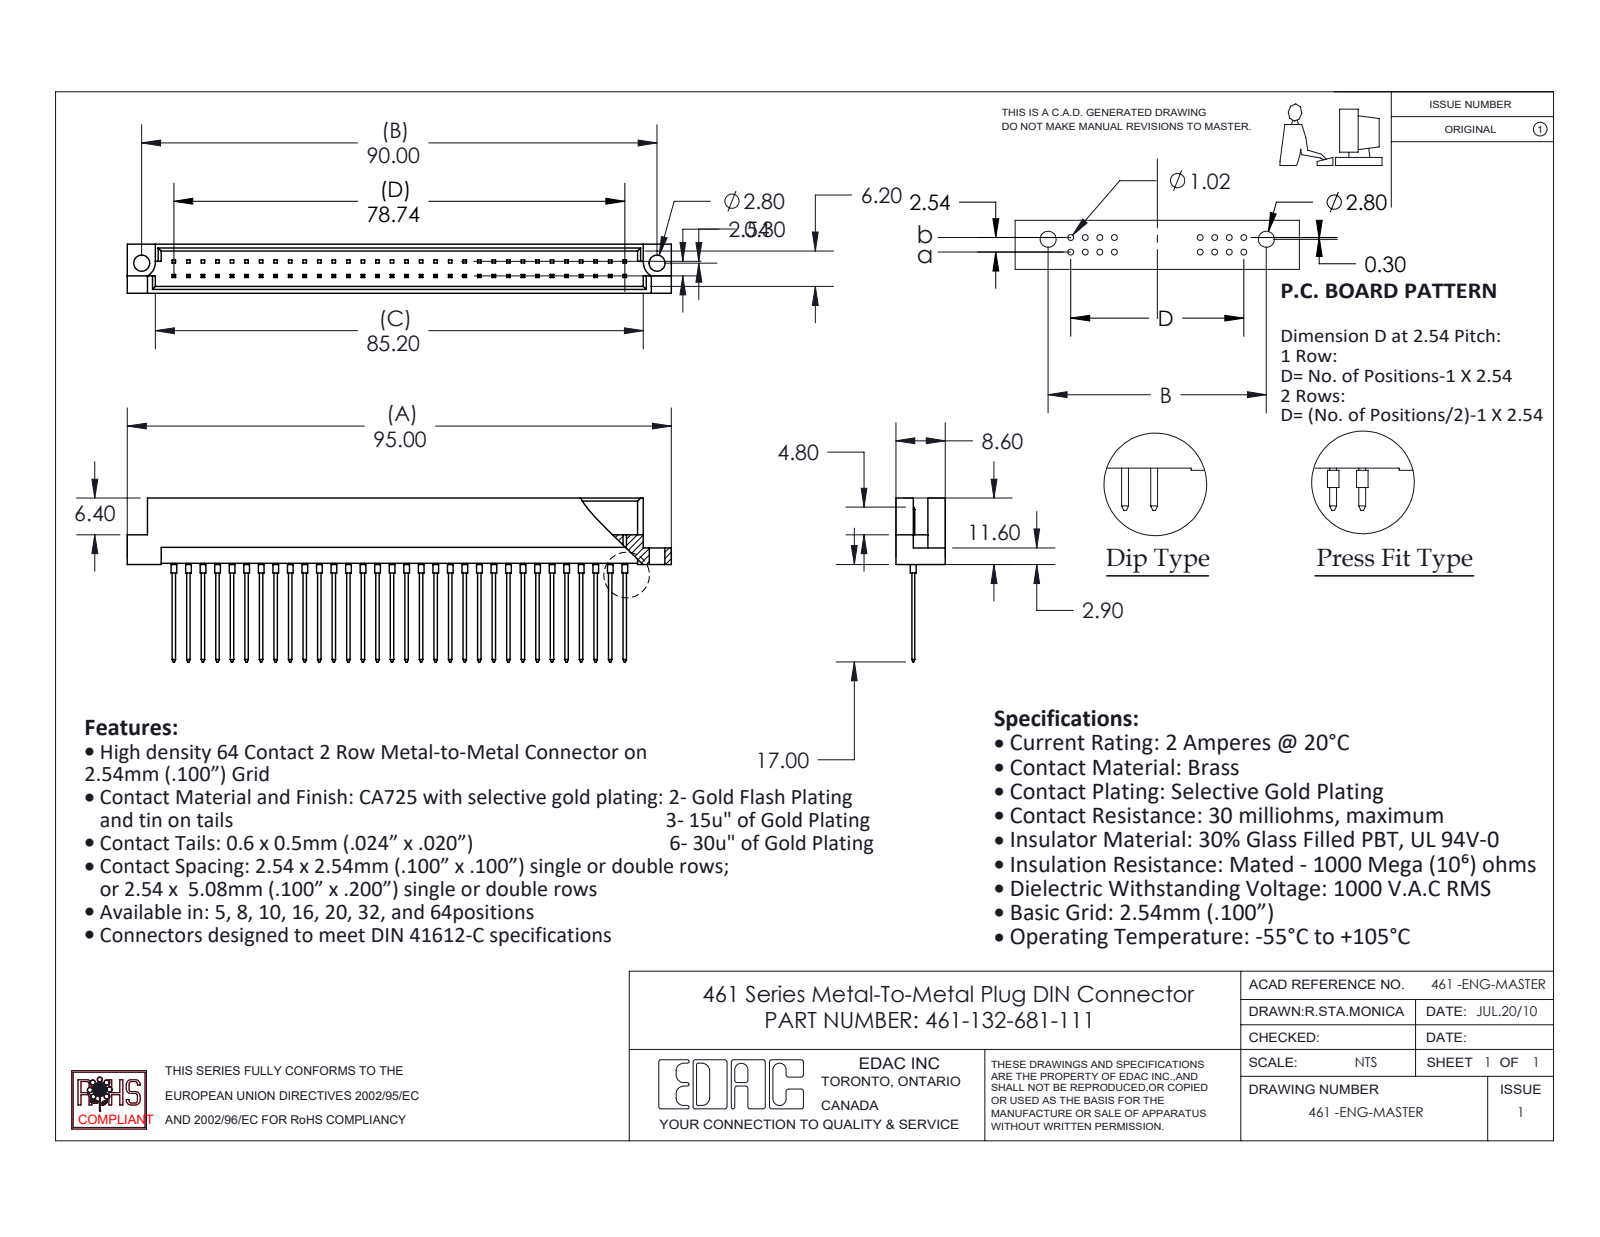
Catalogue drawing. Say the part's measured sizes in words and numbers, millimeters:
The part is named "461-290_81; 461-132-681-111; 461 Part_64". Its 3-D file was written by "SolidWorks 2020 (CONFIG_CONTROL_DESIGN)". It is 33 solids with 1009 faces: 938 planar, 71 cylindrical and 0 other. Overall it measures 95 by 28.6 by 8.6 millimeters. Its volume is 4 936 cubic millimeters and its surface area 7 636 square millimeters. Round holes: 2 of diameter 2.8. Round bosses or shafts: 32 of diameter 1. Partial cylindrical surfaces (rounded edges, fillets, slot ends): 2 of radius 2.8. The main face-to-face distances are 1.2, 7.4, 8.6, 6.2, 3.28, 5.32, 2.08, 4.12, 2.78, 5.82. The hole center spacings are 90.
